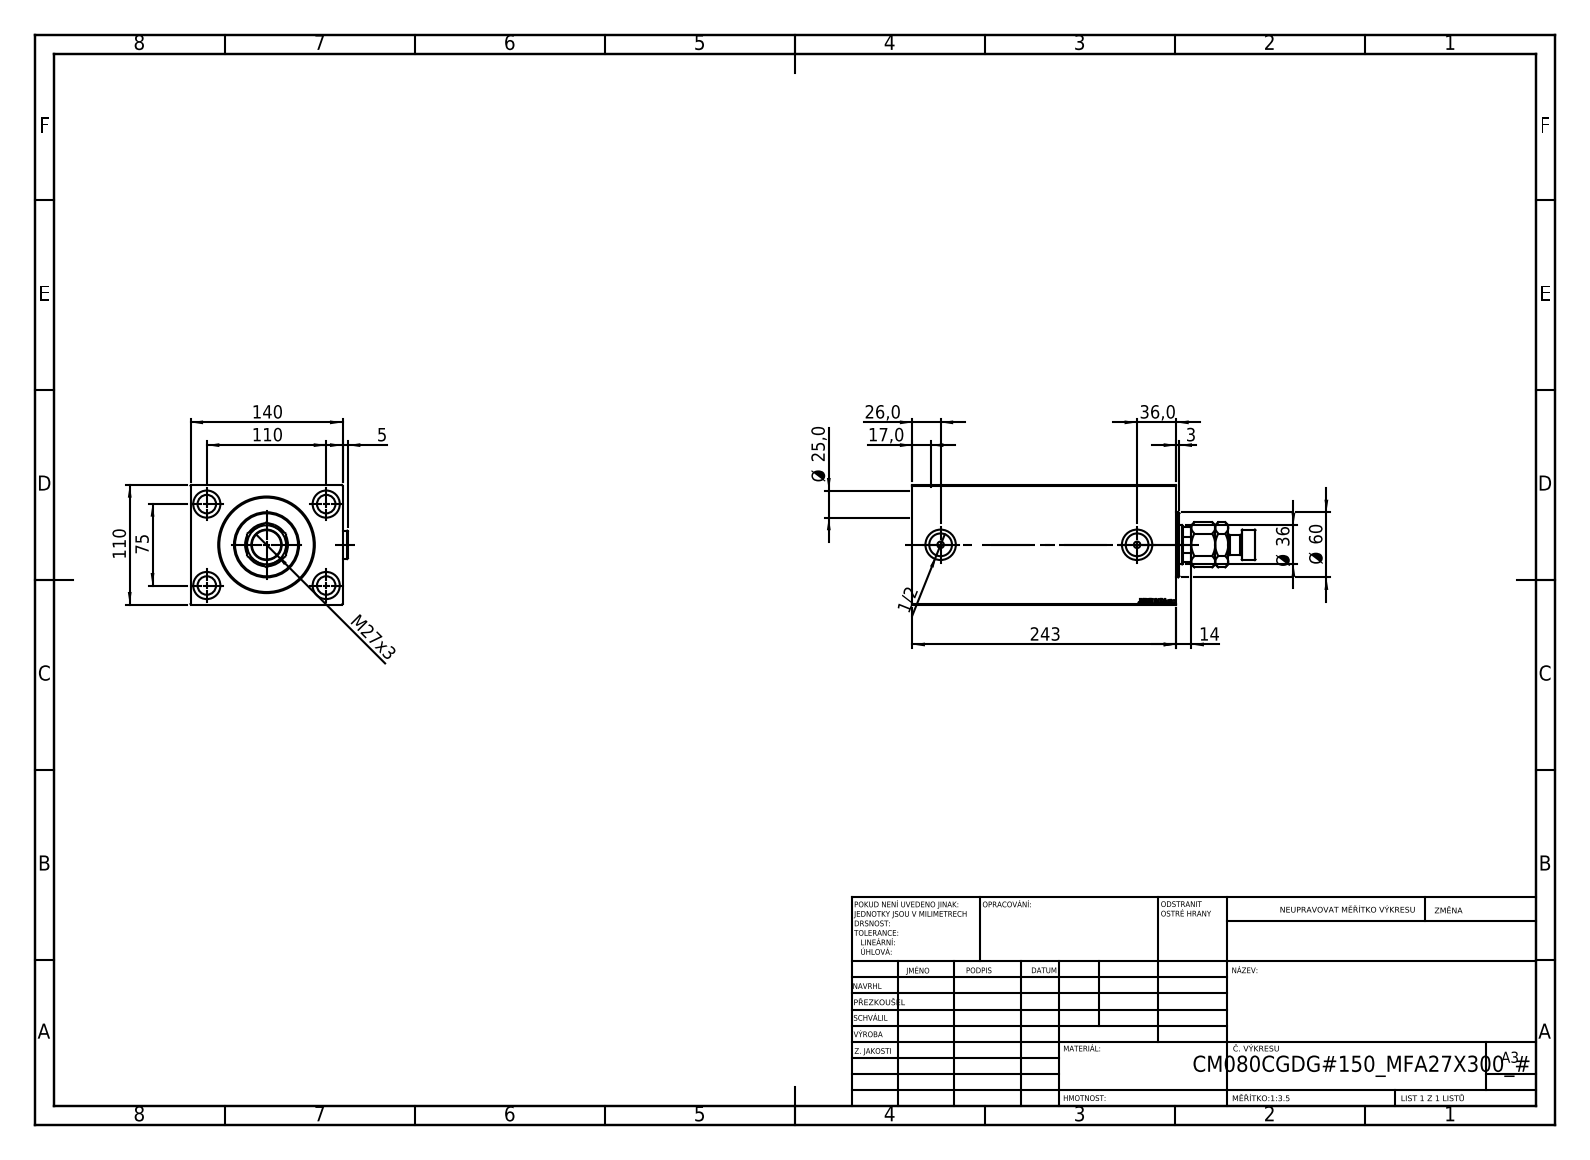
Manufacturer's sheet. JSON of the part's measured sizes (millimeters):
{"part_name": "V450CM_VC_B; V450CM_C_Body; Zatka_OIL_PORT; MFA (+1 more)", "step_written_by": "SolidWorks 2019 (CONFIG_CONTROL_DESIGN)", "units": "millimeters", "bodies": {"solids": 6, "faces": 971, "planar": 459, "cylindrical": 82, "other": 430}, "overall_size": [316, 144.9, 110], "volume_mm3": 2918000, "surface_area_mm2": 341096, "round_holes": [[17, 4], [25, 4], [6, 2], [20.96, 2], [28, 2], [25.5, 1], [36, 1], [39.5, 1], [80, 1], [82, 1], [87, 1]], "round_bosses_or_shafts": [[26, 2], [60, 1], [28, 1], [18, 1]], "partial_cylinders_radius": [[17.5, 1]], "face_to_face_distances": [110, 140, 243, 222, 21, 14, 229, 208, 164, 150], "hole_center_spacings": [66.57, 75, 110, 133.14, 181]}
